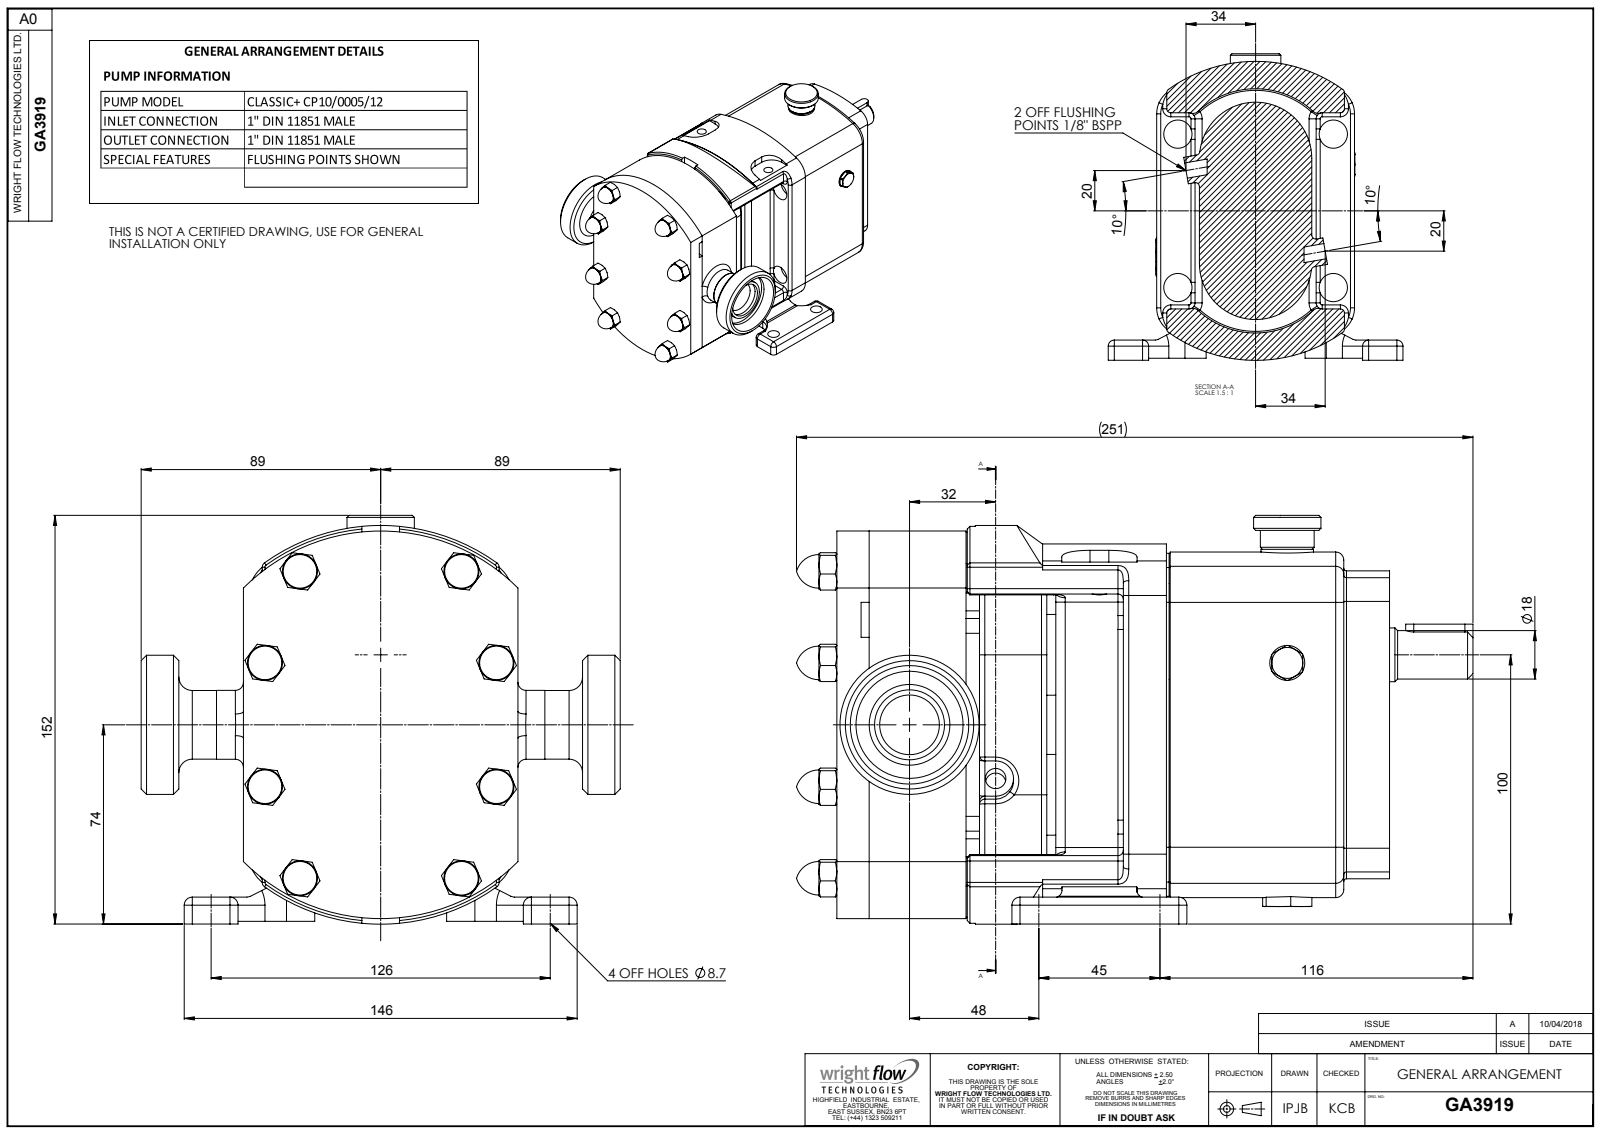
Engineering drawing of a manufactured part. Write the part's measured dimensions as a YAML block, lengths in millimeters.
part_name: "GA3919; Copy of Z94-5031-11 - 1 INCH DIN11851^GA3919; Copy of CP10-0005-12 H T^GA3919"
step_written_by: "SolidWorks 2023 (AUTOMOTIVE_DESIGN)"
units: millimeters
bodies: {solids: 3, faces: 749, planar: 256, cylindrical: 224, other: 269}
overall_size: [251.35, 178, 151.87]
volume: 2264000
surface_area: 182112
round_holes:
  - {diameter: 8.7, count: 4}
  - {diameter: 14, count: 4}
  - {diameter: 6.8, count: 2}
  - {diameter: 7.63, count: 2}
  - {diameter: 22.2, count: 1}
  - {diameter: 22.3, count: 1}
  - {diameter: 22.53, count: 1}
  - {diameter: 26, count: 1}
  - {diameter: 39.8, count: 1}
round_bosses_or_shafts:
  - {diameter: 30, count: 3}
  - {diameter: 51.7, count: 1}
  - {diameter: 25.6, count: 1}
  - {diameter: 25.5, count: 1}
  - {diameter: 25.02, count: 1}
  - {diameter: 19.99, count: 1}
  - {diameter: 19.98, count: 1}
  - {diameter: 19.5, count: 1}
partial_cylinders:
  - {radius: 2, count: 32}
  - {radius: 3, count: 24}
  - {radius: 13.5, count: 12}
  - {radius: 10.5, count: 8}
  - {radius: 3.5, count: 6}
  - {radius: 5.5, count: 4}
  - {radius: 6, count: 4}
  - {radius: 9, count: 4}
face_to_face_distances: [5, 124, 205.35, 91.99, 81.35, 96.99, 102, 97, 5.01, 2]
hole_center_spacings: [35.92, 100.55, 45, 76, 77.02, 108.2, 126, 133.79]
